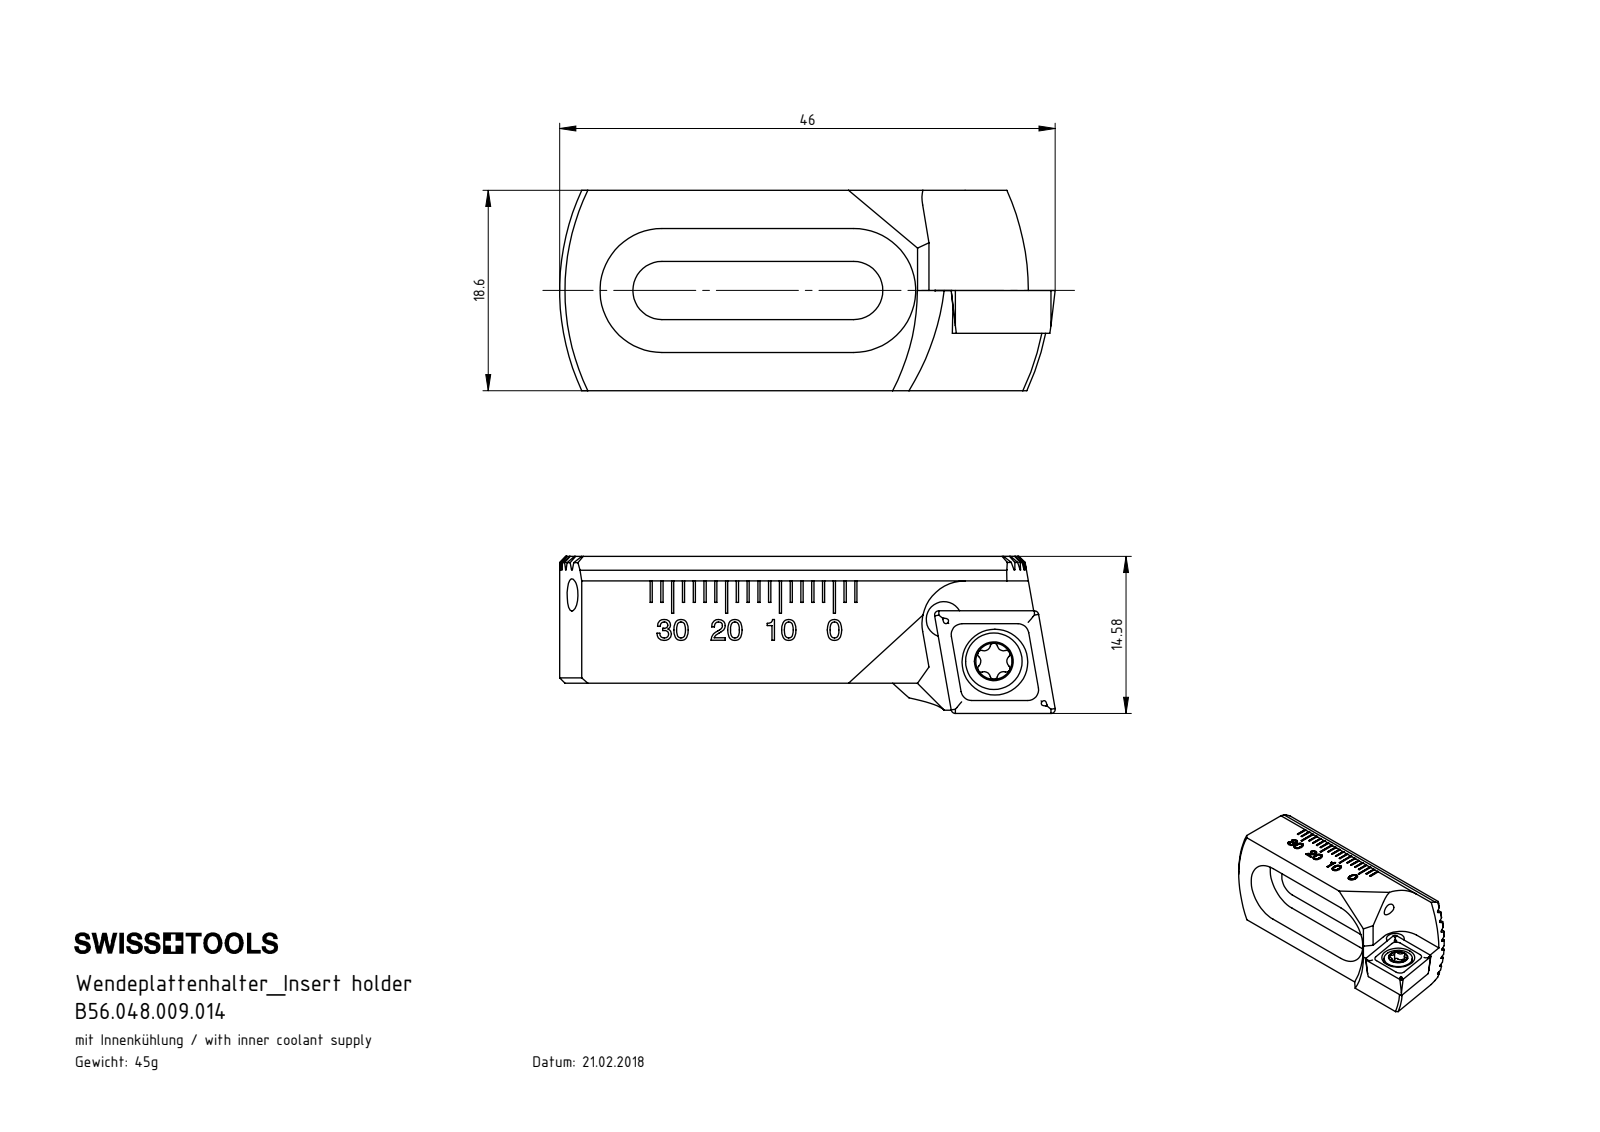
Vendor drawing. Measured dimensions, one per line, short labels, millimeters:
name: CCMT09T304; KVT_MB_600_030; BV2-WCB.K11.014_B; WCB-ER2.001.009_A (+1 more)
written by: SolidWorks 2017 (CONFIG_CONTROL_DESIGN)
unit: mm
bodies: 5 solids, 444 faces (210 planar, 77 cylindrical, 157 other)
size: 46 × 18.6 × 14.58
volume: 5 758 mm³; area: 4 615 mm²
holes: 3× ⌀2, 2× ⌀3.3, 1× ⌀2.38, 1× ⌀4.4, 1× ⌀6.1
bosses: 1× ⌀5.25, 1× ⌀4, 1× ⌀3
rounds: 10× R0.14, 6× R0.34, 6× R0.59, 2× R2.7, 2× R5.75, 1× R4, 1× R22, 1× R23
face distances: 1.73, 3.46, 8.66, 10.39, 6.93, 18.6, 12.12, 12, 6.6, 5.2
hole spacings: 6.35, 6.47
